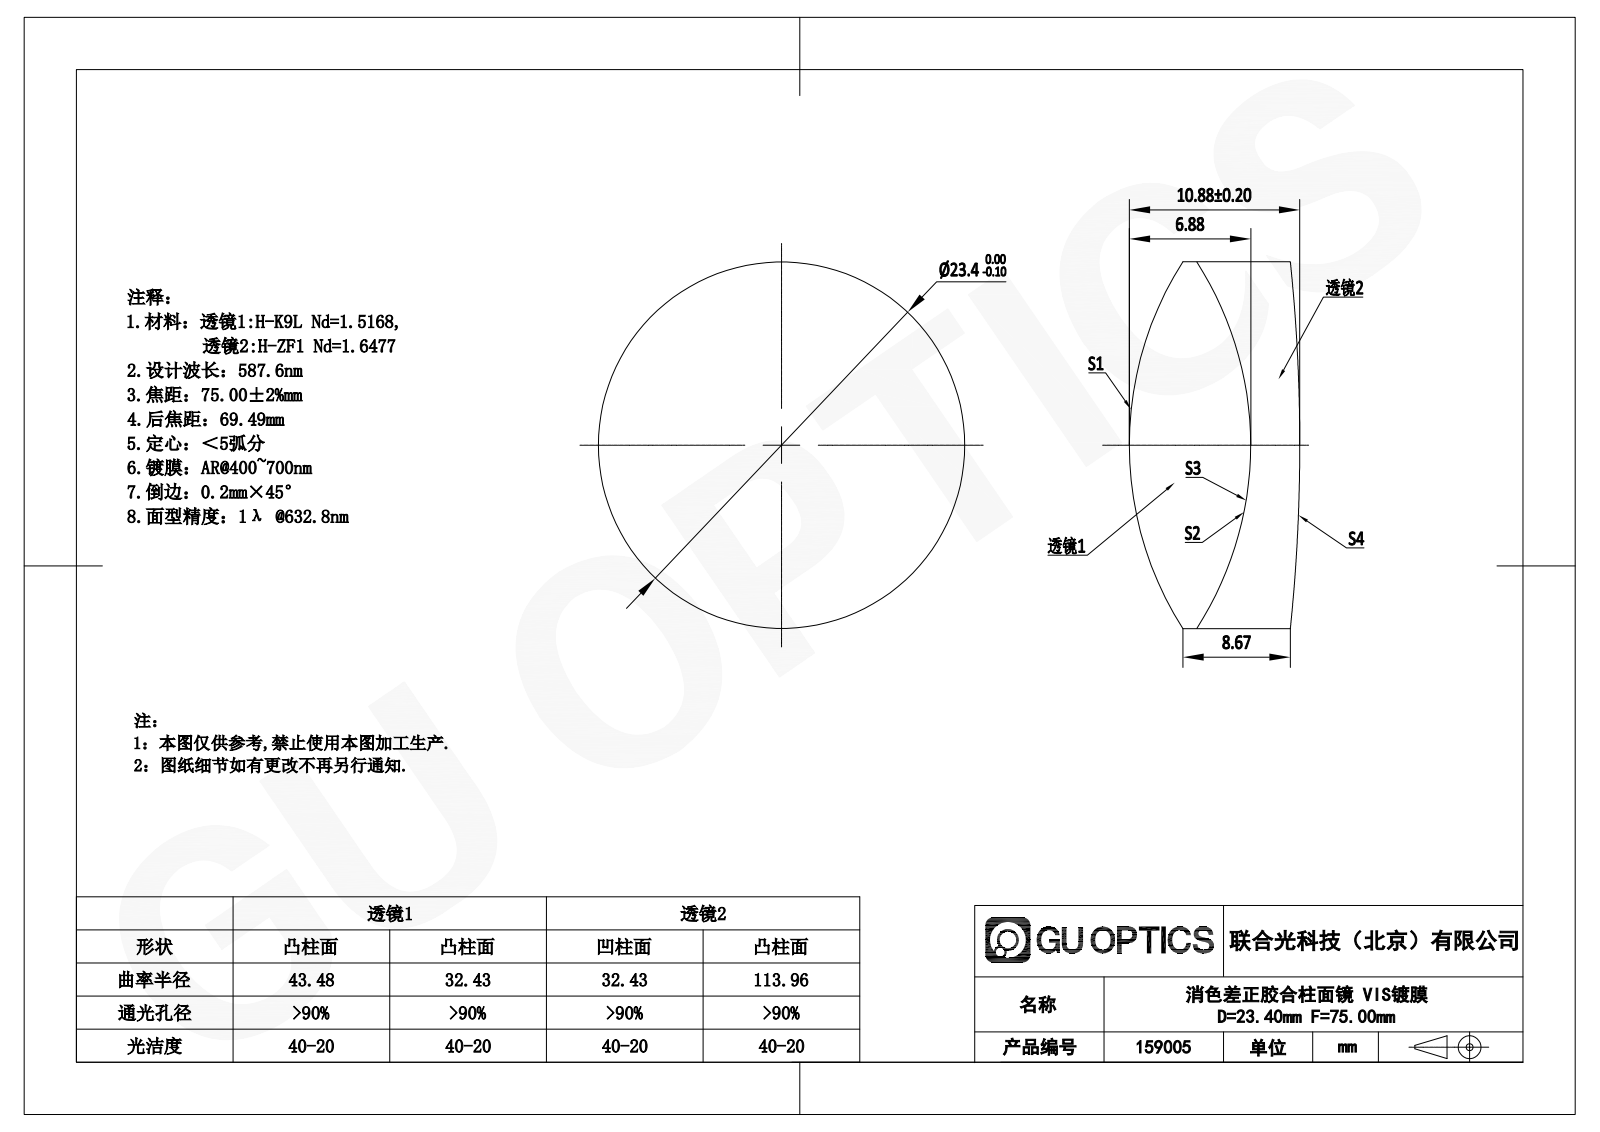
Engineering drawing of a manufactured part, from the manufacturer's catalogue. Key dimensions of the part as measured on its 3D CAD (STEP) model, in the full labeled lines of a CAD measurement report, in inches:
Part name (STEP PRODUCT): 159005
STEP written by: SolidWorks 2020 (CONFIG_CONTROL_DESIGN)
Units: inches
Bodies: 1 solid, 5 faces (0 planar, 5 cylindrical, 0 other)
Overall size (bounding box): 0.921 × 0.921 × 0.428
Volume: 0.26 in³ · Surface area: 2.376 in²
Round bosses / shafts (diameter × count): ⌀0.921 ×1
Partial cylindrical surfaces — rounded edges, fillets, slot ends (radius × count): R0.856 ×1, R4.487 ×1
